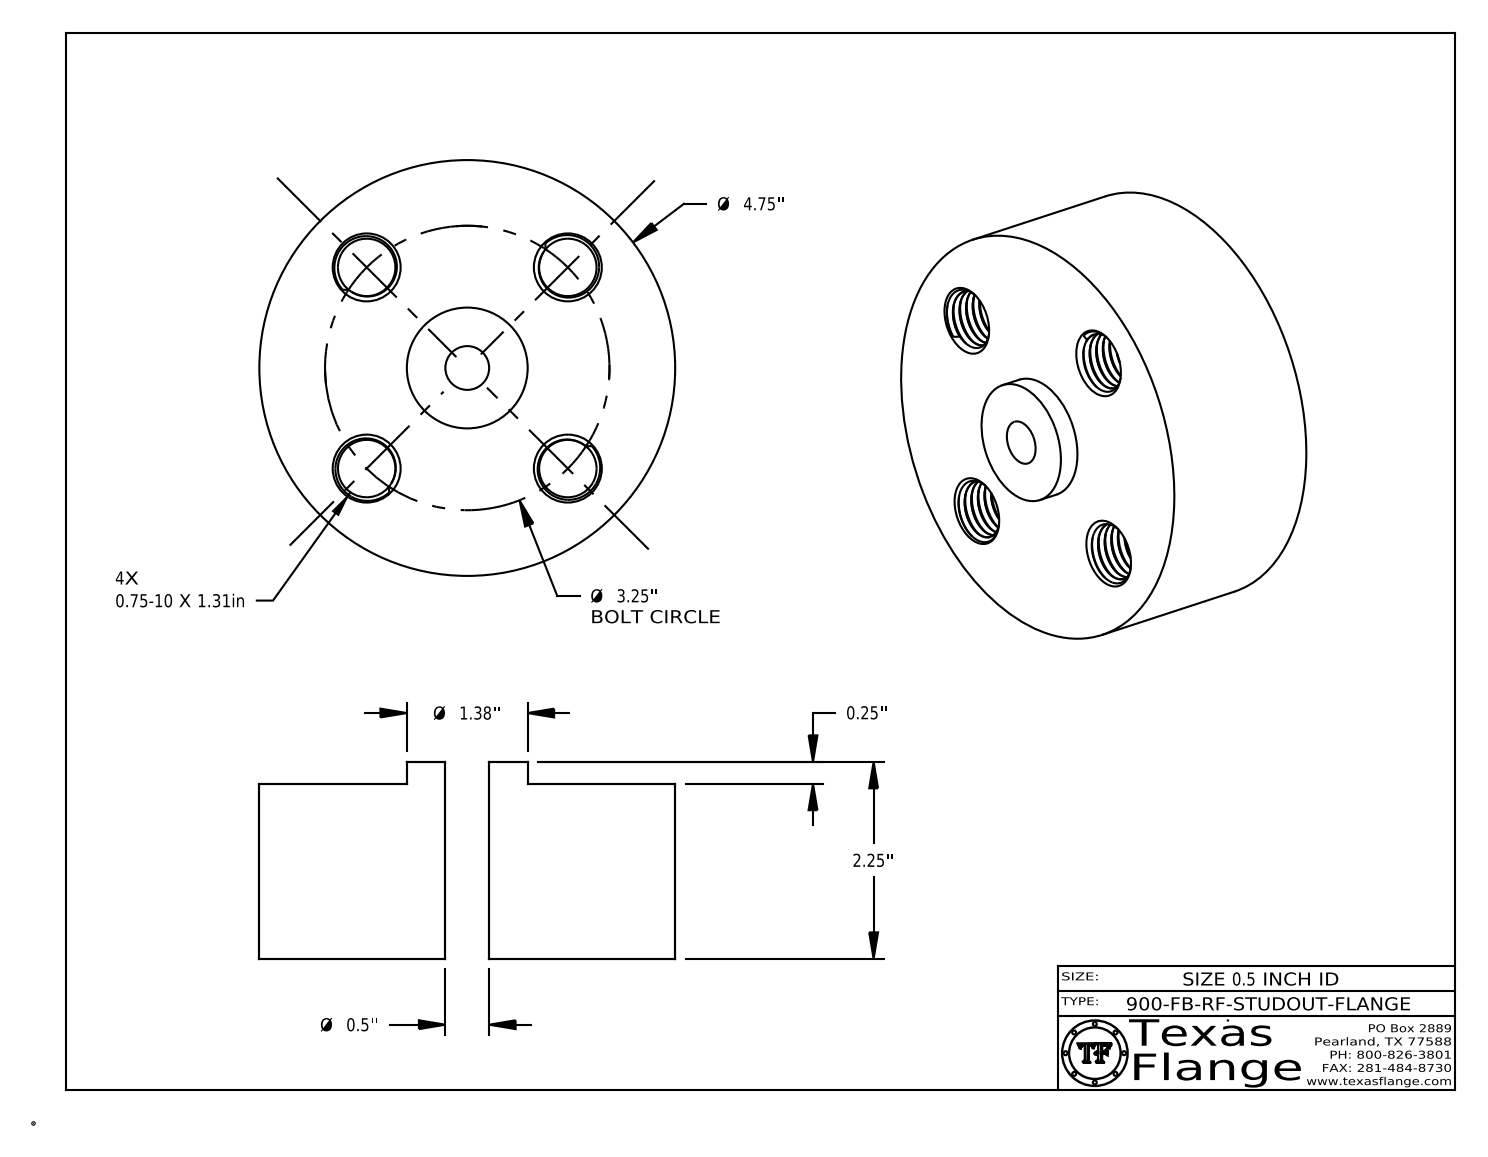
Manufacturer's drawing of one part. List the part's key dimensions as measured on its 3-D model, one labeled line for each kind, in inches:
Part name (STEP PRODUCT): 0.5-900-FB-RF-STUDOUT-FLANGE
STEP written by: CATIA V5 STEP AP214 (AUTOMOTIVE_DESIGN)
Units: inches
Bodies: 1 solid, 634 faces (368 planar, 106 cylindrical, 160 other)
Overall size (bounding box): 4.75 × 4.75 × 2.25
Volume: 33.34 in³ · Surface area: 83.49 in²
Round holes (diameter × count): ⌀0.656 ×4, ⌀0.5 ×1, ⌀1 ×1
Round bosses / shafts (diameter × count): ⌀0.061 ×8, ⌀4.75 ×1, ⌀1.38 ×1, ⌀0.788 ×1
Main face-to-face distances: 2, 0.25, 2.25, 0.015, 2.235, 1.985, 0.298, 0.292, 0.054, 0.248
Hole centre spacings: 1.625, 2.298, 1.244, 3.003, 3.25
